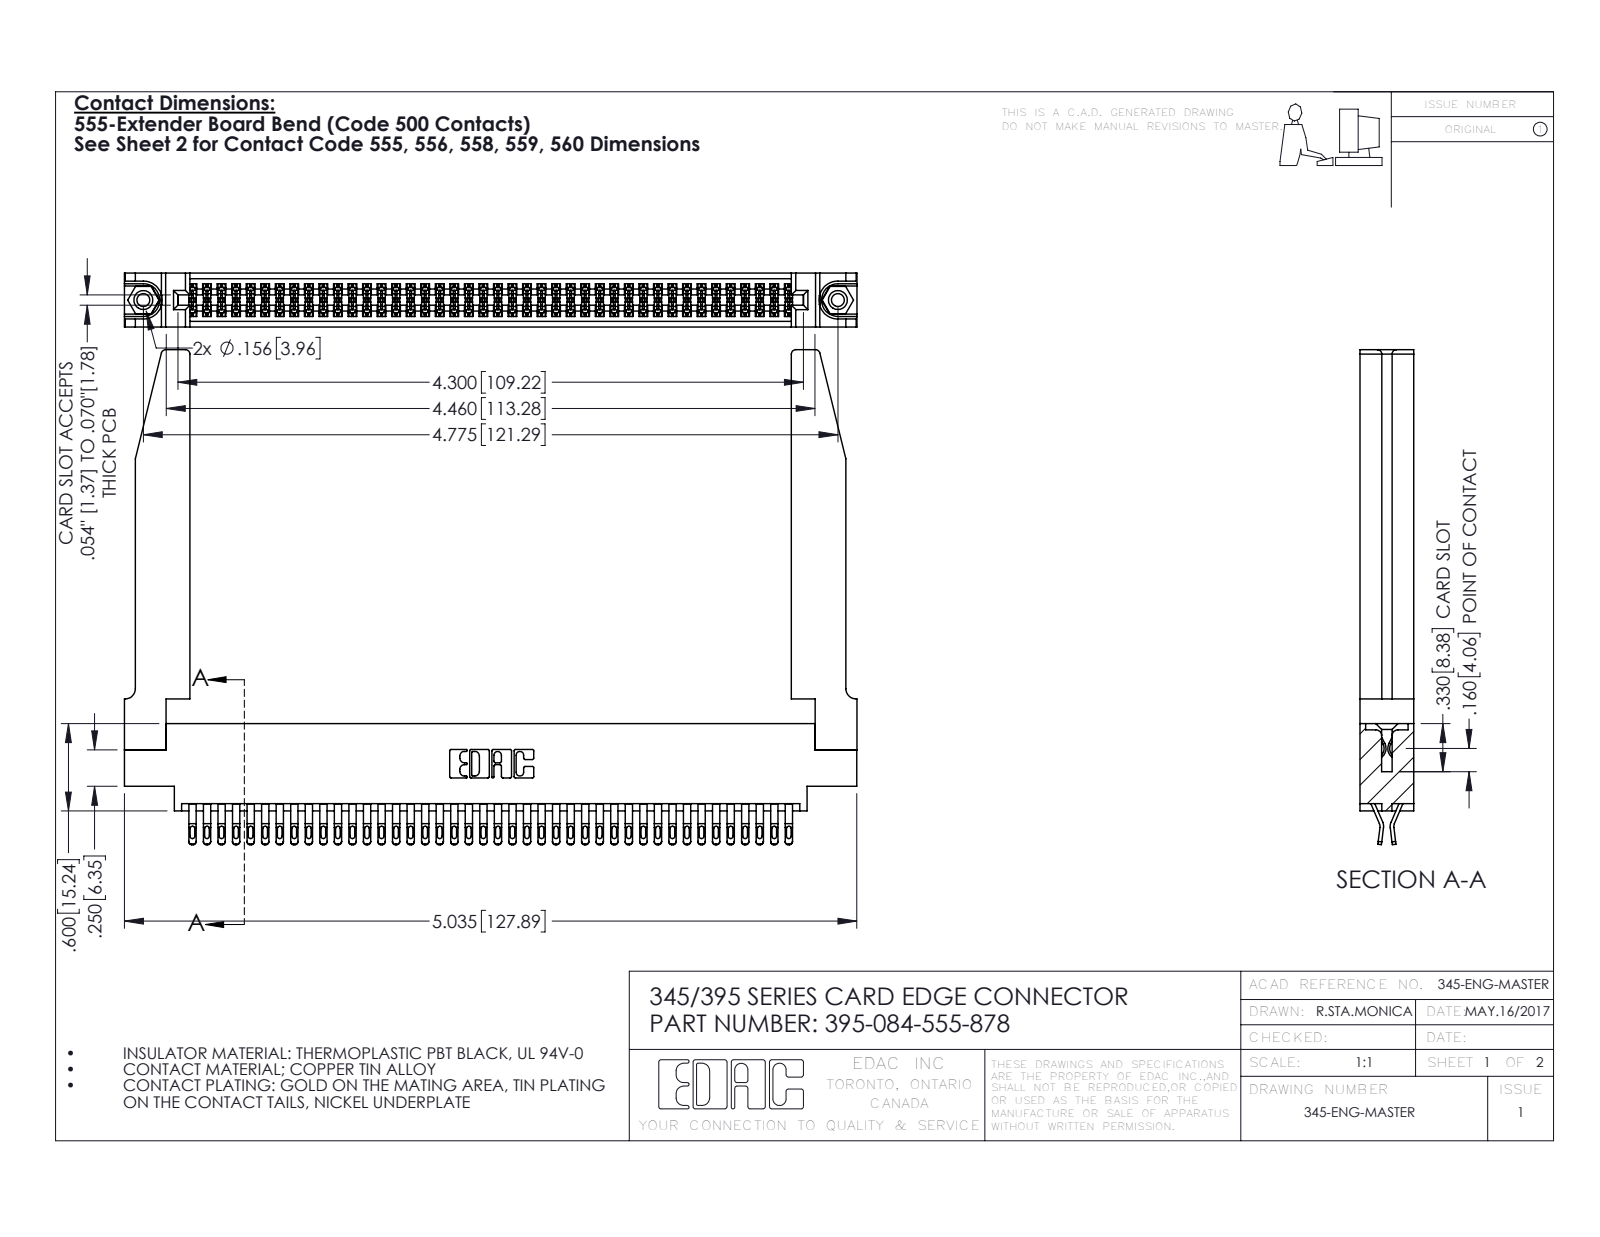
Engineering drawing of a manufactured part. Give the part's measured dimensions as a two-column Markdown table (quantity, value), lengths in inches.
| quantity | value |
| --- | --- |
| part name | 345 Part_0.170 Offset - 0.156 Dia-TH; 395-084-555-878; 345-250-001_345-250-001-102; 345-220-078_345-220-078 (+1 more) |
| STEP written by | SolidWorks 2016 (CONFIG_CONTROL_DESIGN) |
| units | inches |
| bodies | 89 solids, 5068 faces (2830 planar, 2186 cylindrical, 52 other) |
| overall size | 5.036 × 3.402 × 0.37 |
| volume | 1.24 in³ |
| surface area | 40.9 in² |
| round holes (diameter × count) | 0.089 × 2, 0.125 × 2, 0.156 × 2, 0.064 × 1 |
| round bosses / shafts (diameter × count) | 0.155 × 2 |
| partial cylindrical surfaces (radius × count) | 0.016 × 210, 0.02 × 168, 0.006 × 126, 0.01 × 22, 0.03 × 8, 0.007 × 6, 0.031 × 6, 0.026 × 3 |
| main face-to-face distances | 0.37, 0.072, 0.298, 0.025, 0.098, 0.272, 0.2, 0.225, 0.175, 0.148 |
| hole center spacings | 0.27, 4.539, 4.775 |
